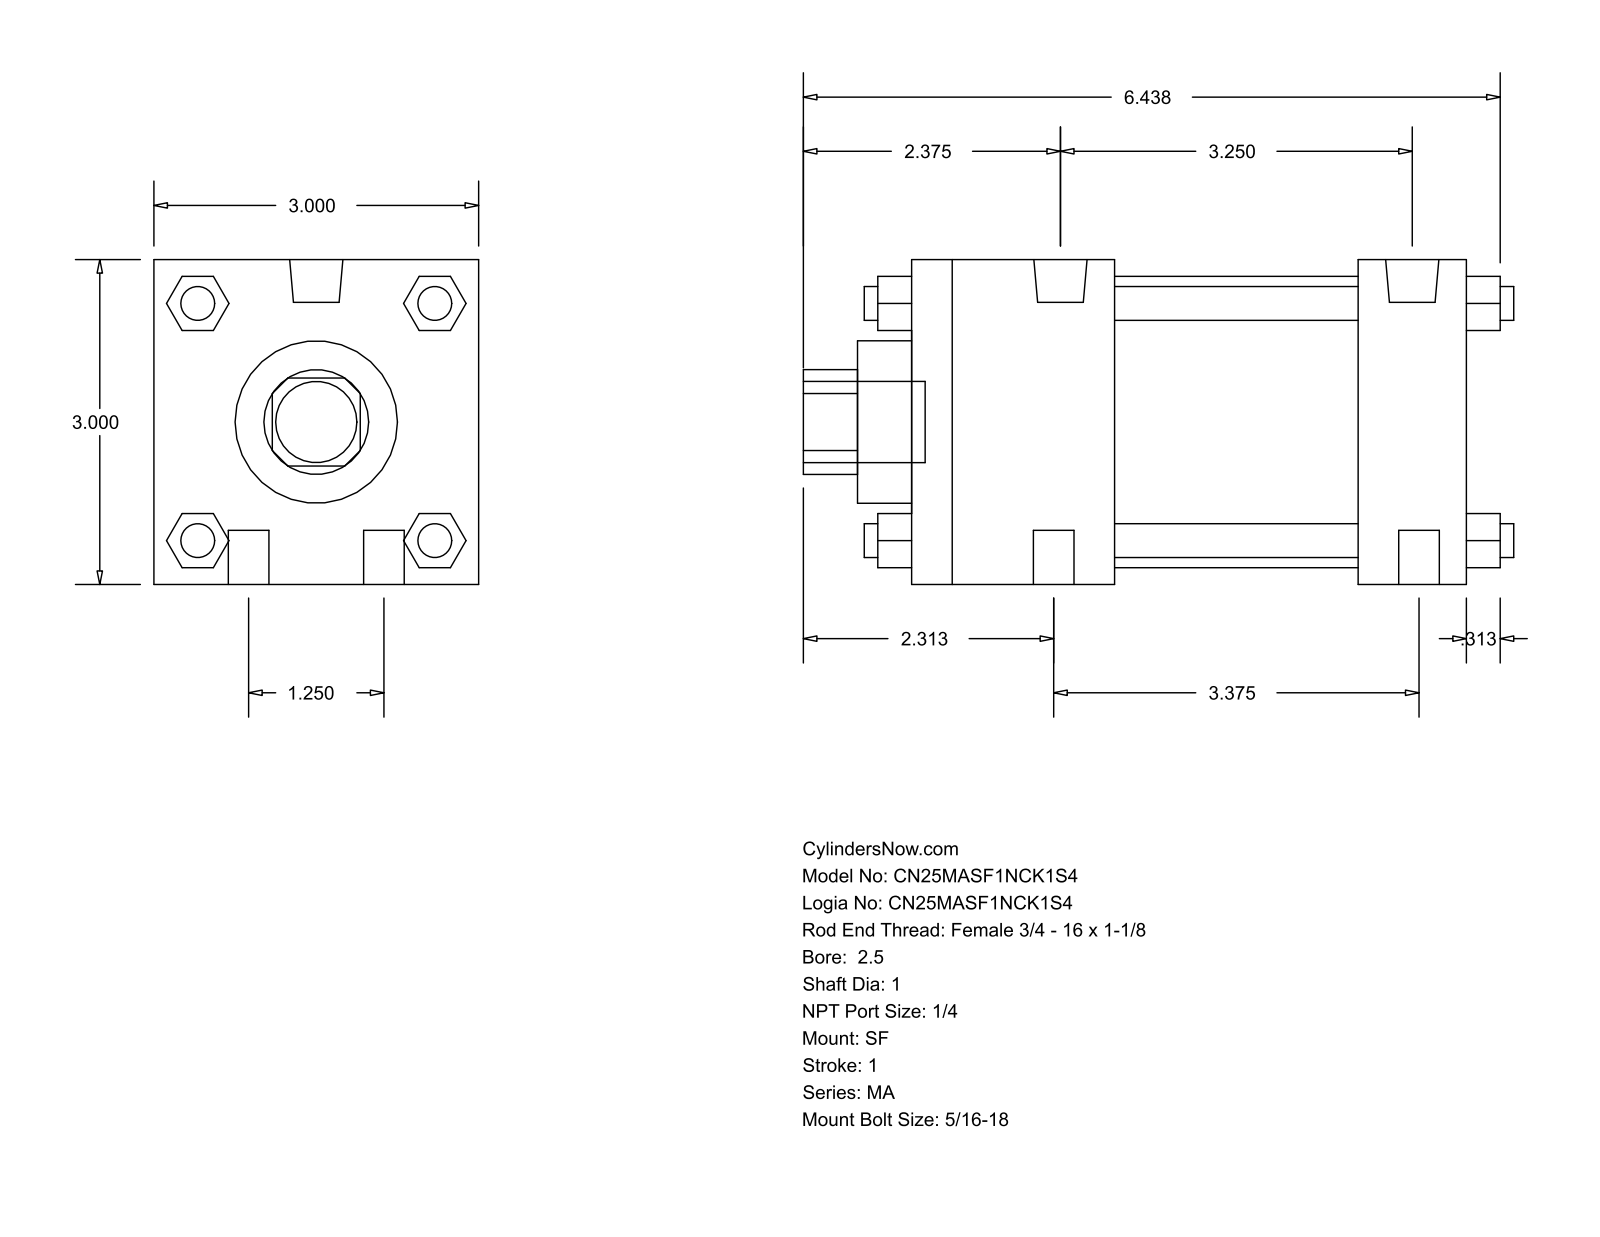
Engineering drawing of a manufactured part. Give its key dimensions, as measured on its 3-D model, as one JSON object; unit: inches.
{"part_name": "MA_SF__0250_1", "step_written_by": "GSSL Pune (CONFIG_CONTROL_DESIGN)", "units": "inches", "bodies": {"solids": 0, "faces": 124, "planar": 94, "cylindrical": 30, "other": 0}, "overall_size": [6.563, 3, 3], "round_holes": [[1, 1], [1.5, 1], [2.69, 1]], "round_bosses_or_shafts": [[0.313, 6], [0.375, 4], [0.492, 2], [0.75, 1]], "partial_cylinders_radius": [[0.484, 1]], "face_to_face_distances": [3, 5.125, 0.5, 4.125, 1, 1.875, 2.25, 3.25, 1.095, 1.896]}
